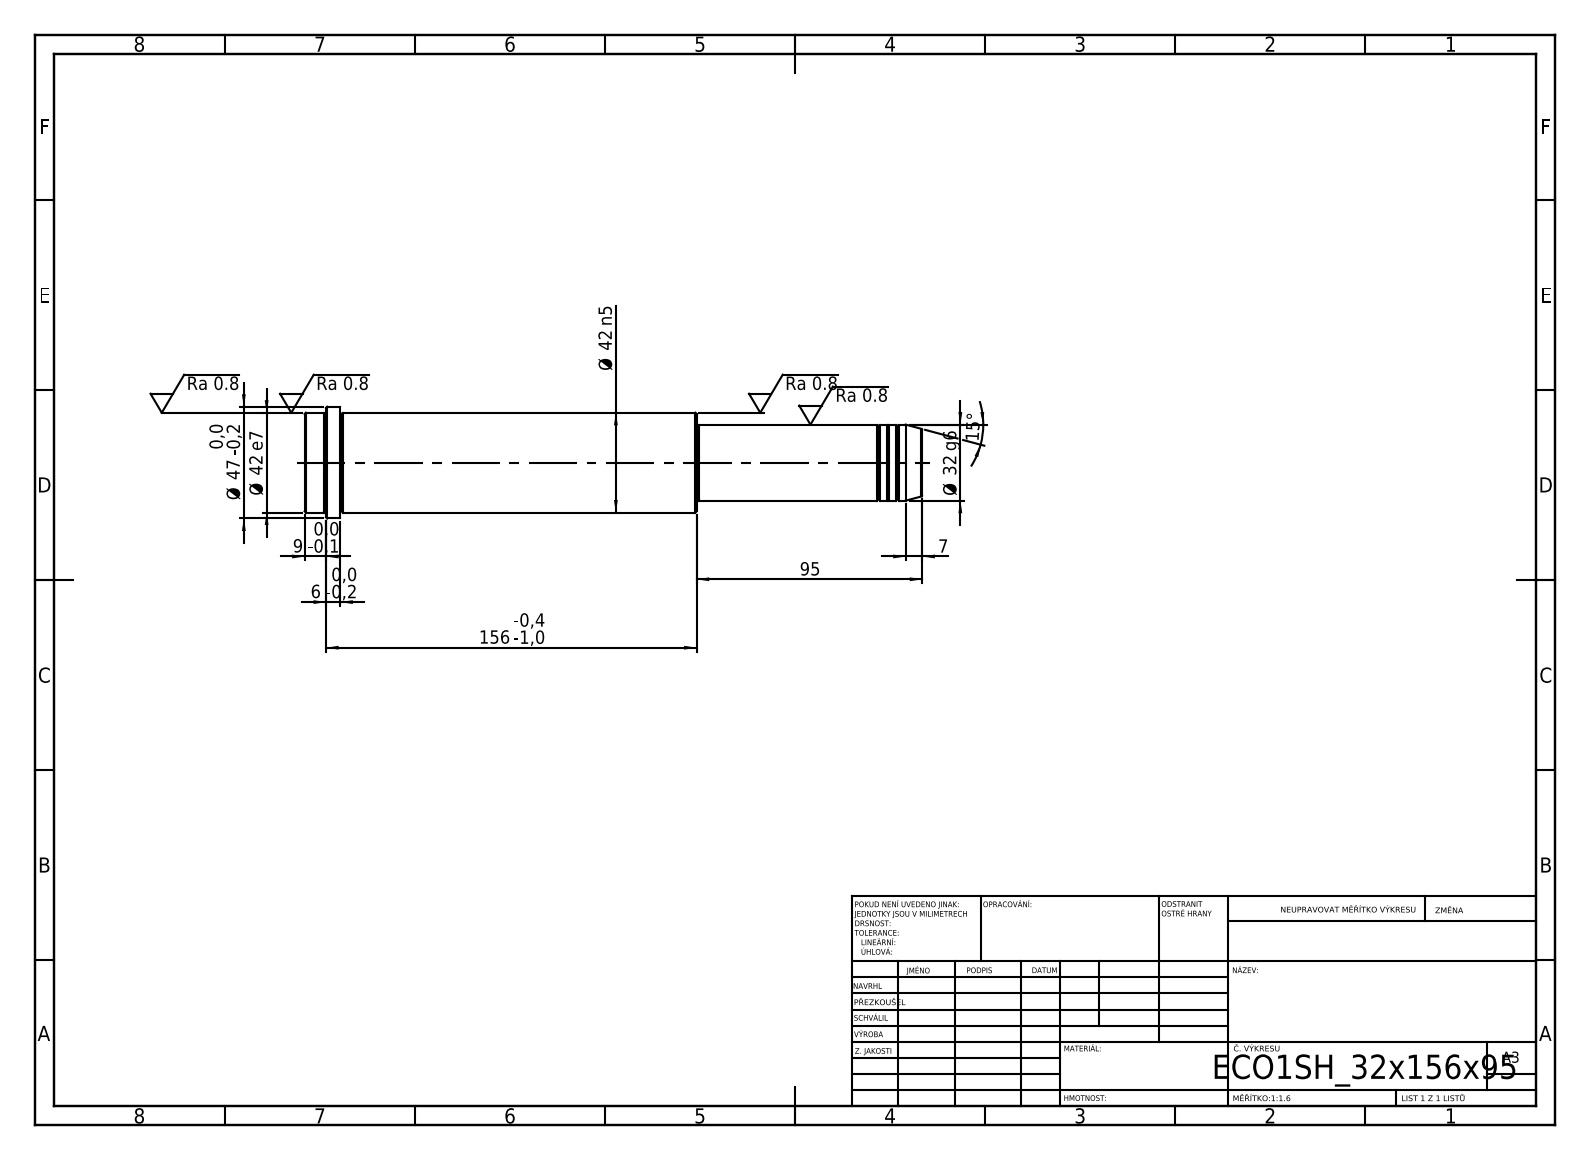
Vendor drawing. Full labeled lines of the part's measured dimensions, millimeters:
STEP written by: SolidWorks 2019 (CONFIG_CONTROL_DESIGN)
Units: millimetres
Bodies: 1 solid, 52 faces (6 planar, 16 cylindrical, 30 other)
Overall size (bounding box): 260 × 47 × 47
Volume: 306 142 mm³ · Surface area: 34 962 mm²
Round bosses / shafts (diameter × count): ⌀47 ×1, ⌀42 ×1, ⌀32 ×1, ⌀31 ×1
Main face-to-face distances: 260, 95, 165, 245, 150, 15, 251, 156, 6, 9
